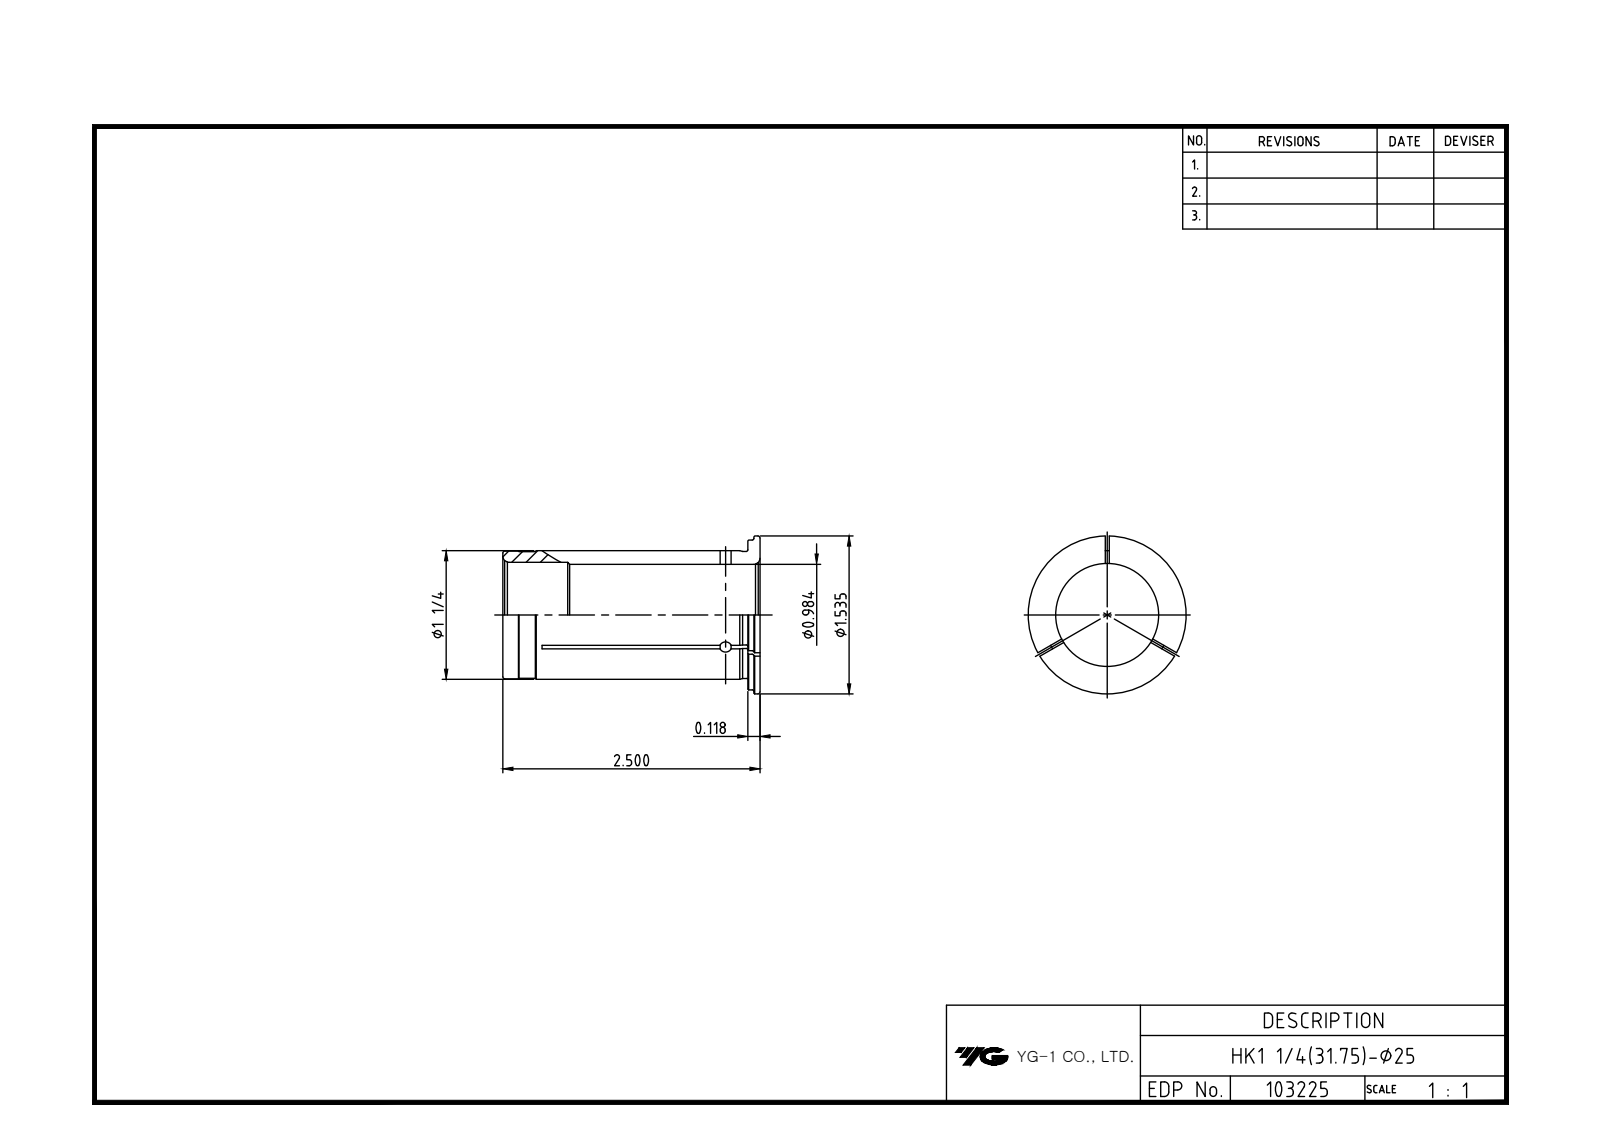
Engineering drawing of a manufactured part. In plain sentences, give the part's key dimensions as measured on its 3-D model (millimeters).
The part is named "LO-HK31.75-25". Its 3-D file was written by "Autodesk Inventor 2025 (AP242_MANAGED_MODEL_BASED_3D_ENGINEERING_MIM_LF)". It is 1 solid with 14 faces: 4 planar, 5 cylindrical and 5 other. Overall it measures 63.5 by 39 by 39 millimeters. Its volume is 19 478 cubic millimeters and its surface area 12 746 square millimeters. Round holes: 1 of diameter 25, 1 of diameter 26. Round bosses or shafts: 1 of diameter 39, 1 of diameter 37, 1 of diameter 31.75. The main face-to-face distances are 63.5, 60.5, 3, 1.5, 62.
